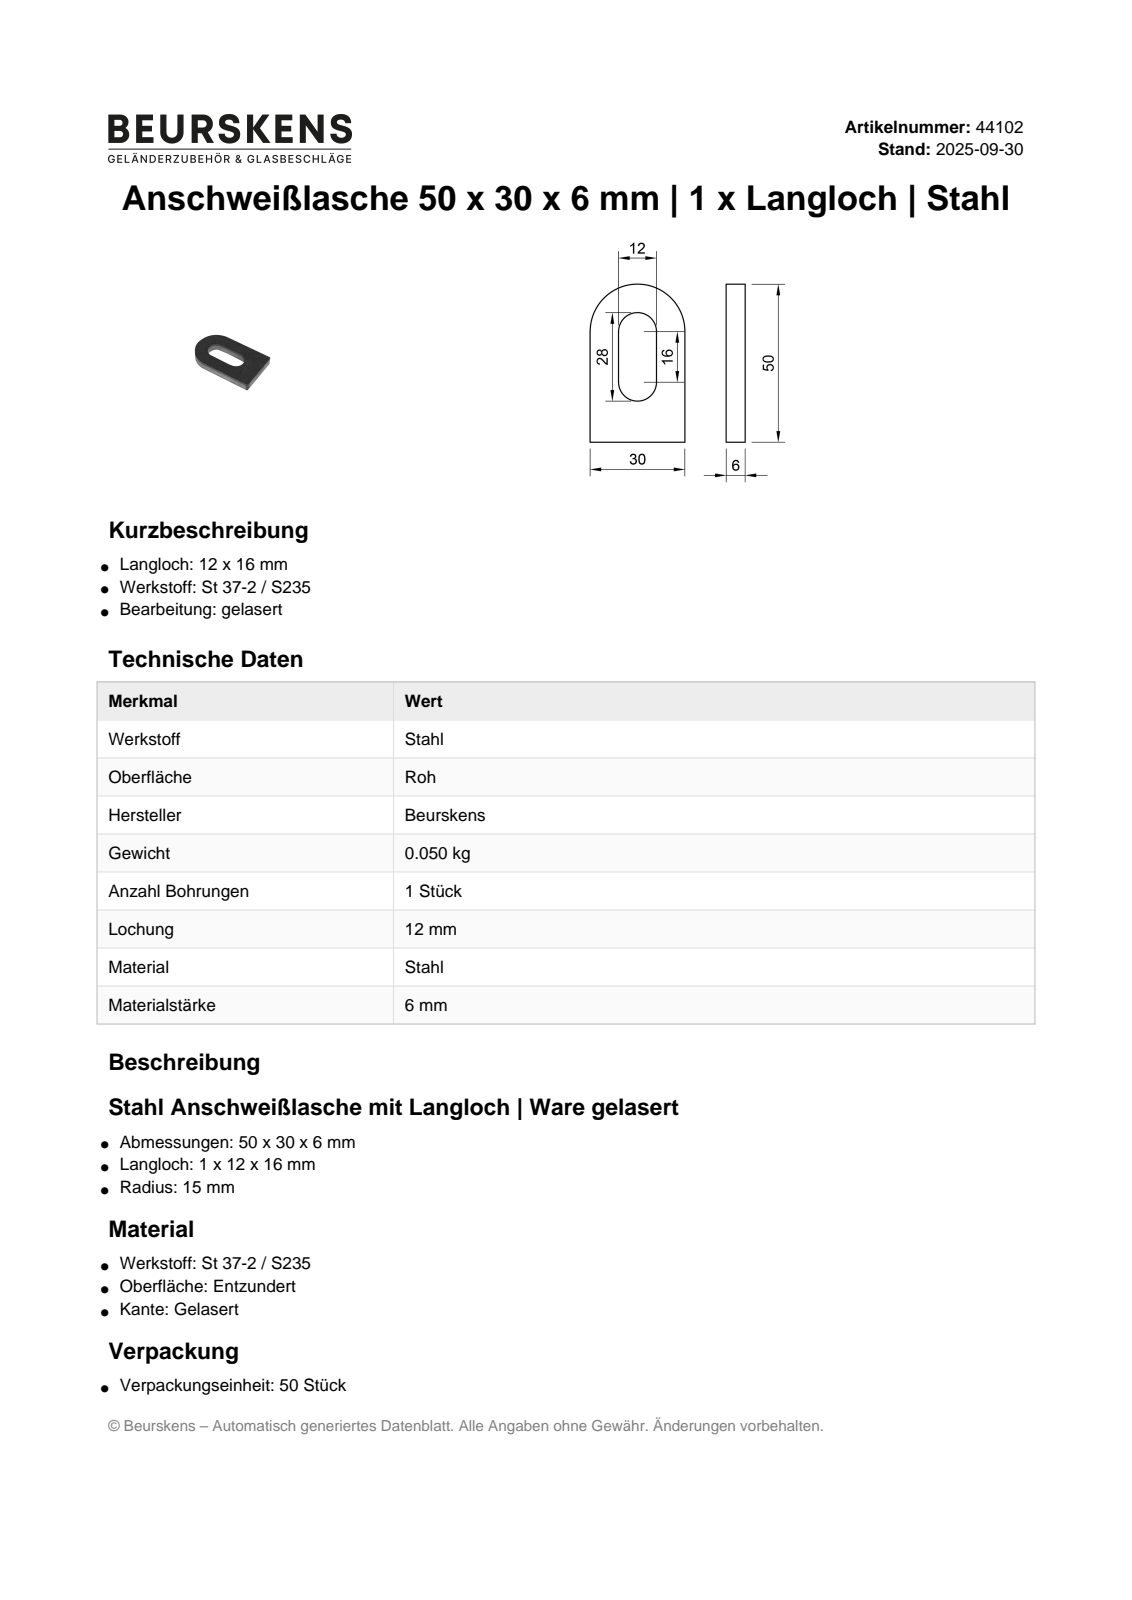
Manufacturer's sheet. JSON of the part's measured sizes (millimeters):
{"part_name": "44102", "step_written_by": "Autodesk Inventor 2023 (AUTOMOTIVE_DESIGN)", "units": "millimeters", "bodies": {"solids": 1, "faces": 10, "planar": 7, "cylindrical": 3, "other": 0}, "overall_size": [50, 30, 6], "volume_mm3": 6590, "surface_area_mm2": 3498, "partial_cylinders_radius": [[6, 2], [15, 1]], "face_to_face_distances": [6, 30, 9, 21, 12]}
